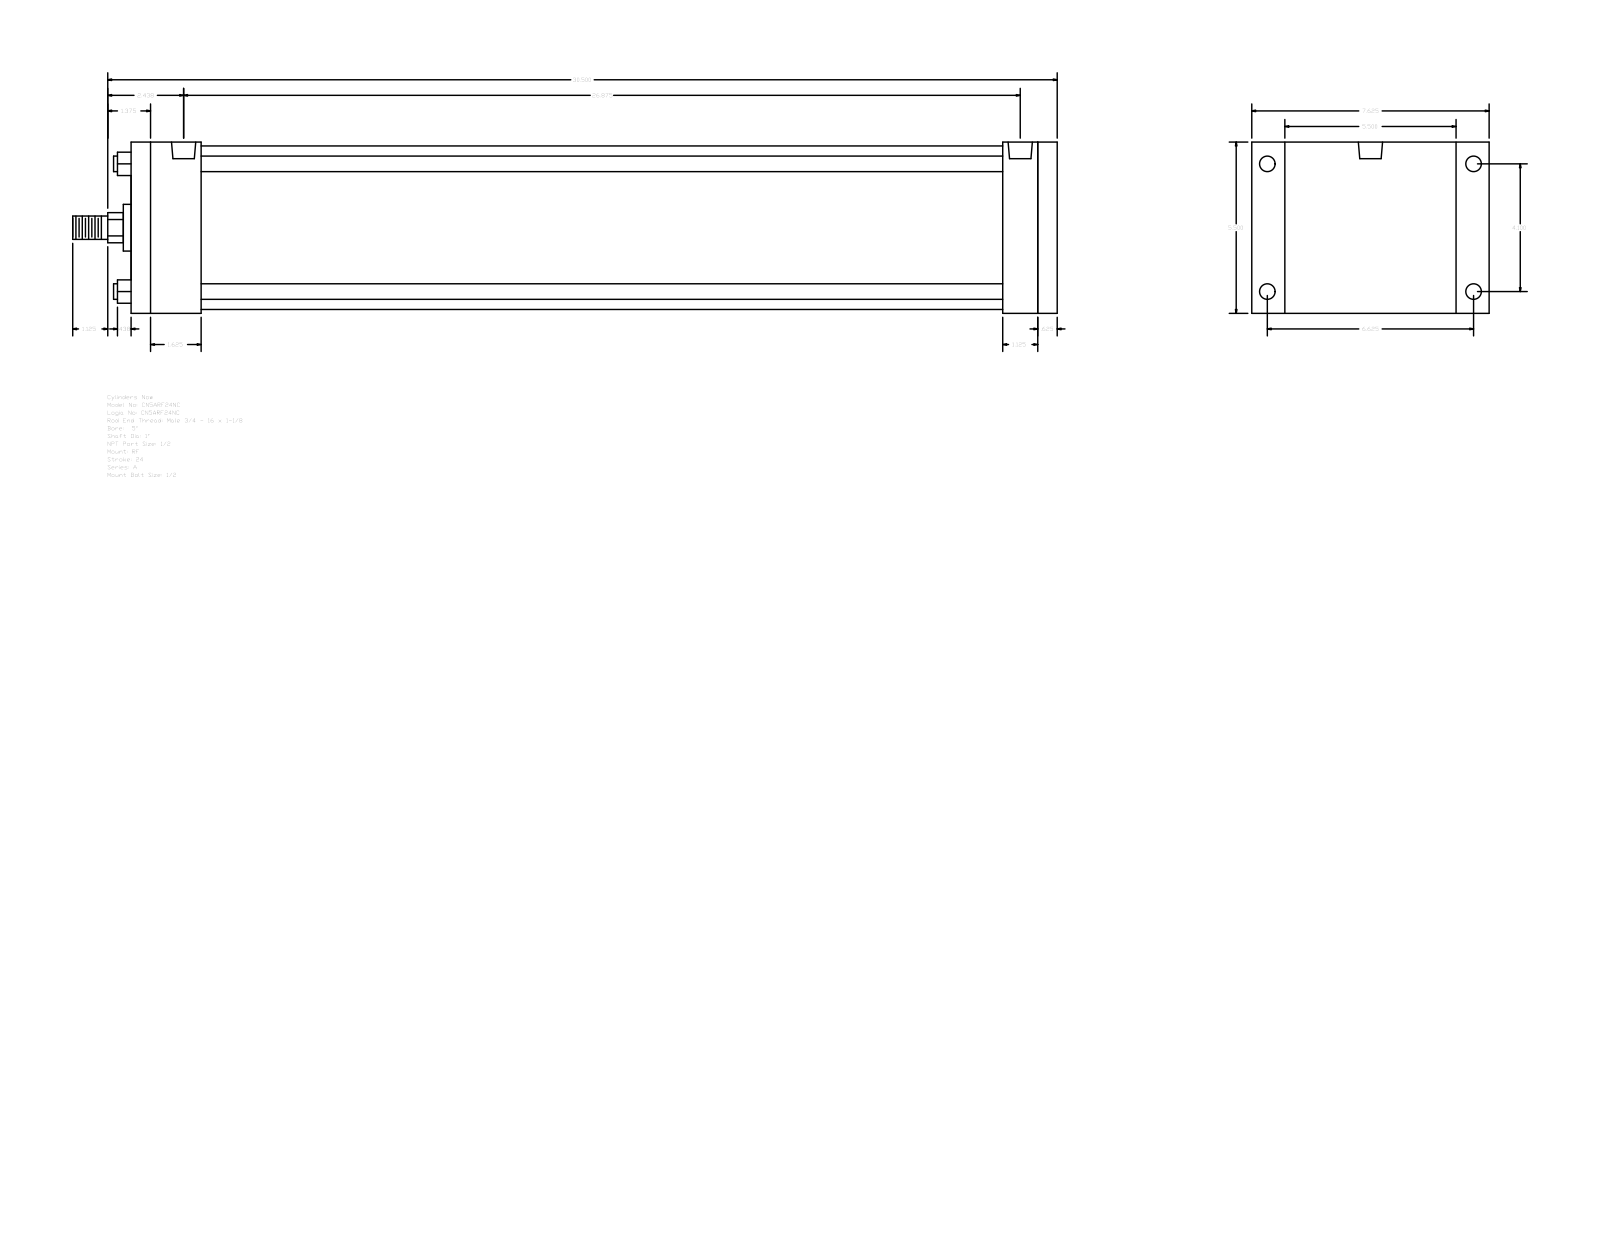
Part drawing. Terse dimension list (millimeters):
name: A_RF__0500_1
written by: GSSL Pune (CONFIG_CONTROL_DESIGN)
unit: mm
bodies: 0 solids, 92 faces (64 planar, 28 cylindrical, 0 other)
size: 803.27 × 193.68 × 139.7
holes: 4× ⌀8.73, 4× ⌀12.7, 2× ⌀19.77
bosses: 4× ⌀12.7, 1× ⌀133.35, 1× ⌀38.1, 1× ⌀25.4, 1× ⌀19.05
rounds: 1× R12.29
face distances: 139.7, 755.65, 739.78, 15.87, 57.15, 682.63, 698.5, 711.2, 654.05, 28.58
hole spacings: 2.39, 104.14, 168.28, 197.9, 677.85, 680.24, 682.63
